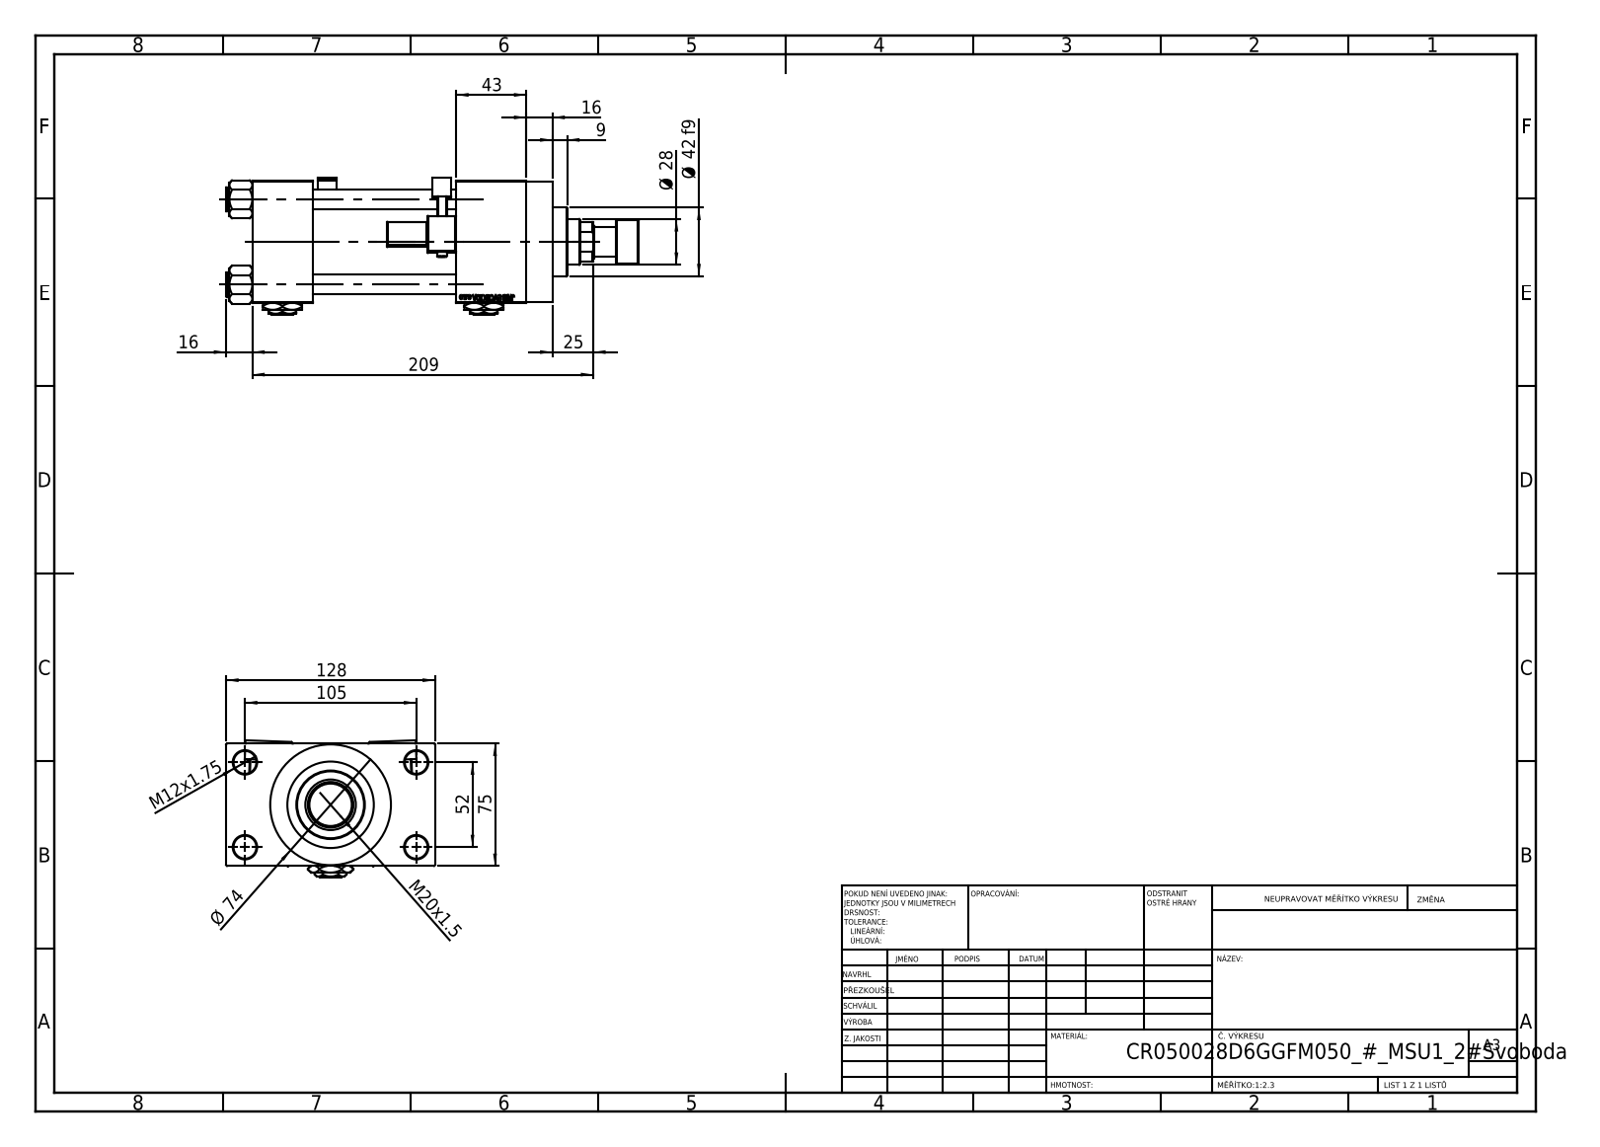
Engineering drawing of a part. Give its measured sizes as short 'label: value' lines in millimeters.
name: V215CR_ROD_END_F; V215CR_D_Body; Zatka_pro_OIL_PORT; V215CR_D_TYCINKA (+4 more)
written by: SolidWorks 2019 (CONFIG_CONTROL_DESIGN)
unit: mm
bodies: 16 solids, 1373 faces (607 planar, 164 cylindrical, 602 other)
size: 253 × 128 × 84.03
volume: 910 652 mm³; area: 205 783 mm²
holes: 4× ⌀12, 4× ⌀14, 2× ⌀7, 2× ⌀20.96, 2× ⌀30, 1× ⌀18.5, 1× ⌀28, 1× ⌀31, 1× ⌀41, 1× ⌀50, 1× ⌀53
bosses: 4× ⌀15, 2× ⌀6, 1× ⌀74, 1× ⌀56, 1× ⌀42, 1× ⌀27, 1× ⌀18
rounds: 48× R0.5, 2× R1, 2× R2.5, 2× R4
face distances: 75, 88, 37, 125, 101.5, 26.5, 168, 131, 43, 16
hole spacings: 26.35, 36.98, 52.3, 58.43, 58.59, 78.65, 94.37, 52
